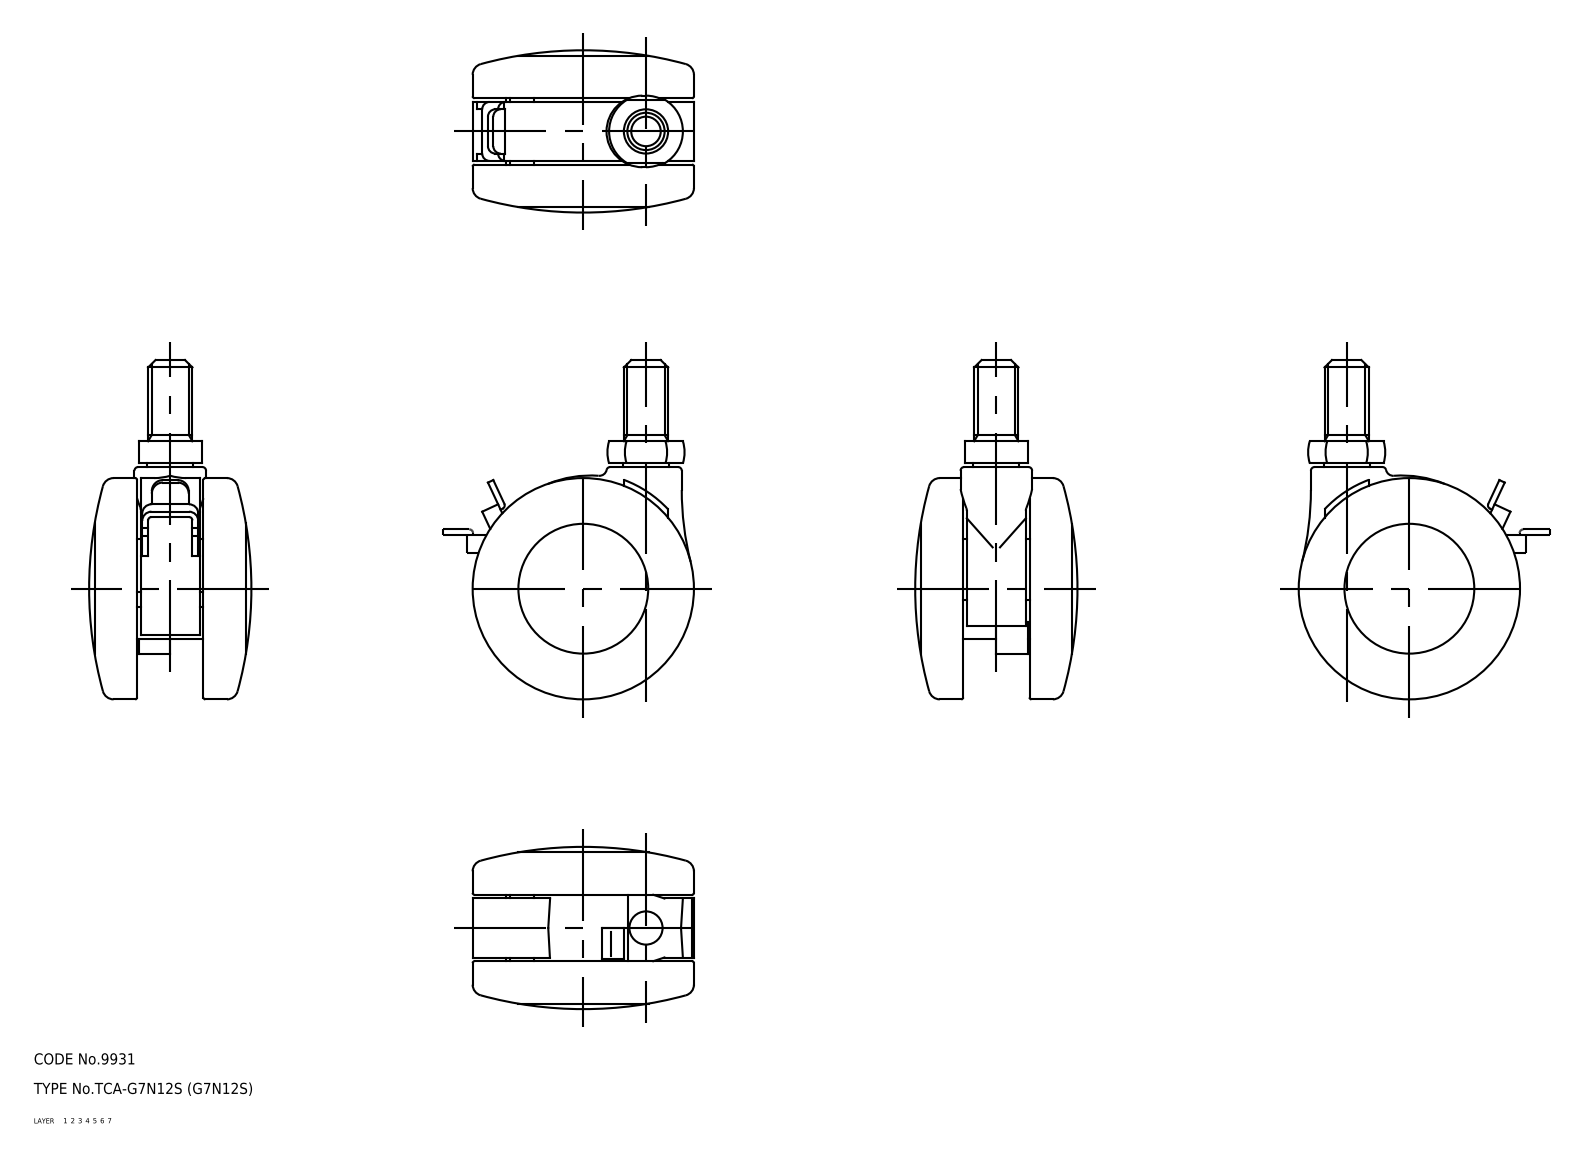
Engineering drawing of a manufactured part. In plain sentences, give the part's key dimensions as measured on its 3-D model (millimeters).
The part is named "wheel; main shaft; lever; G7N12S_13109_36". Its 3-D file was written by "CADfix (AUTOMOTIVE_DESIGN)". It is 5 solids with 194 faces: 0 planar, 0 cylindrical and 194 other. Overall it measures 92 by 68 by 44 millimeters. Its volume is 93 904 cubic millimeters and its surface area 34 434 square millimeters.
